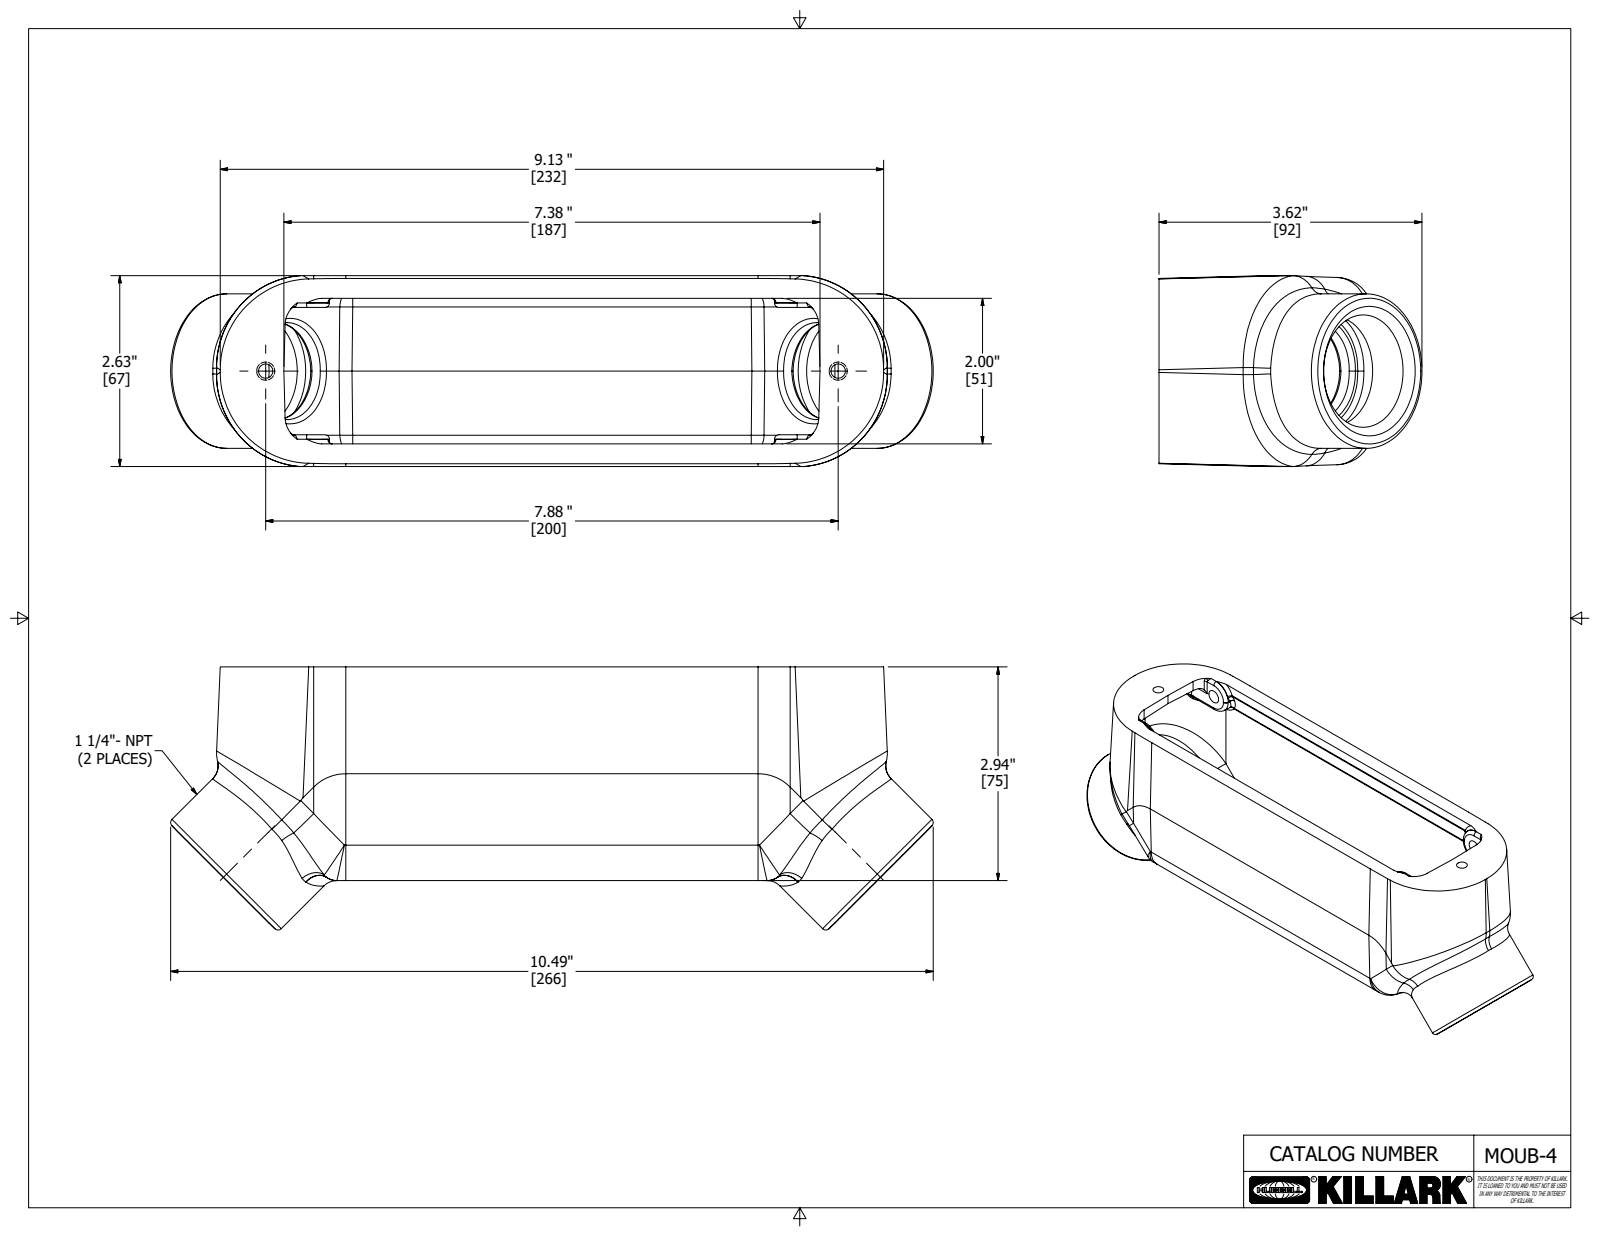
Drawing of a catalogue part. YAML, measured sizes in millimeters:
part_name: "21333-2"
step_written_by: "Autodesk Inventor 2020 (AUTOMOTIVE_DESIGN)"
units: millimeters
bodies: {solids: 1, faces: 699, planar: 288, cylindrical: 94, other: 317}
overall_size: [266.4, 91.9, 66.7]
volume: 284200
surface_area: 111200
round_holes:
  - {diameter: 5, count: 2}
  - {diameter: 33.9, count: 2}
  - {diameter: 42.3, count: 2}
round_bosses_or_shafts:
  - {diameter: 54, count: 2}
partial_cylinders:
  - {radius: 1.6, count: 20}
  - {radius: 6.4, count: 16}
  - {radius: 3.2, count: 10}
  - {radius: 8, count: 8}
  - {radius: 12.7, count: 8}
  - {radius: 9.5, count: 4}
  - {radius: 27, count: 4}
  - {radius: 31.8, count: 4}
face_to_face_distances: [66.7, 57.2, 74.6, 73.8, 0.8, 3.2, 54, 56.4, 0.8, 65.1]
hole_center_spacings: [200]
